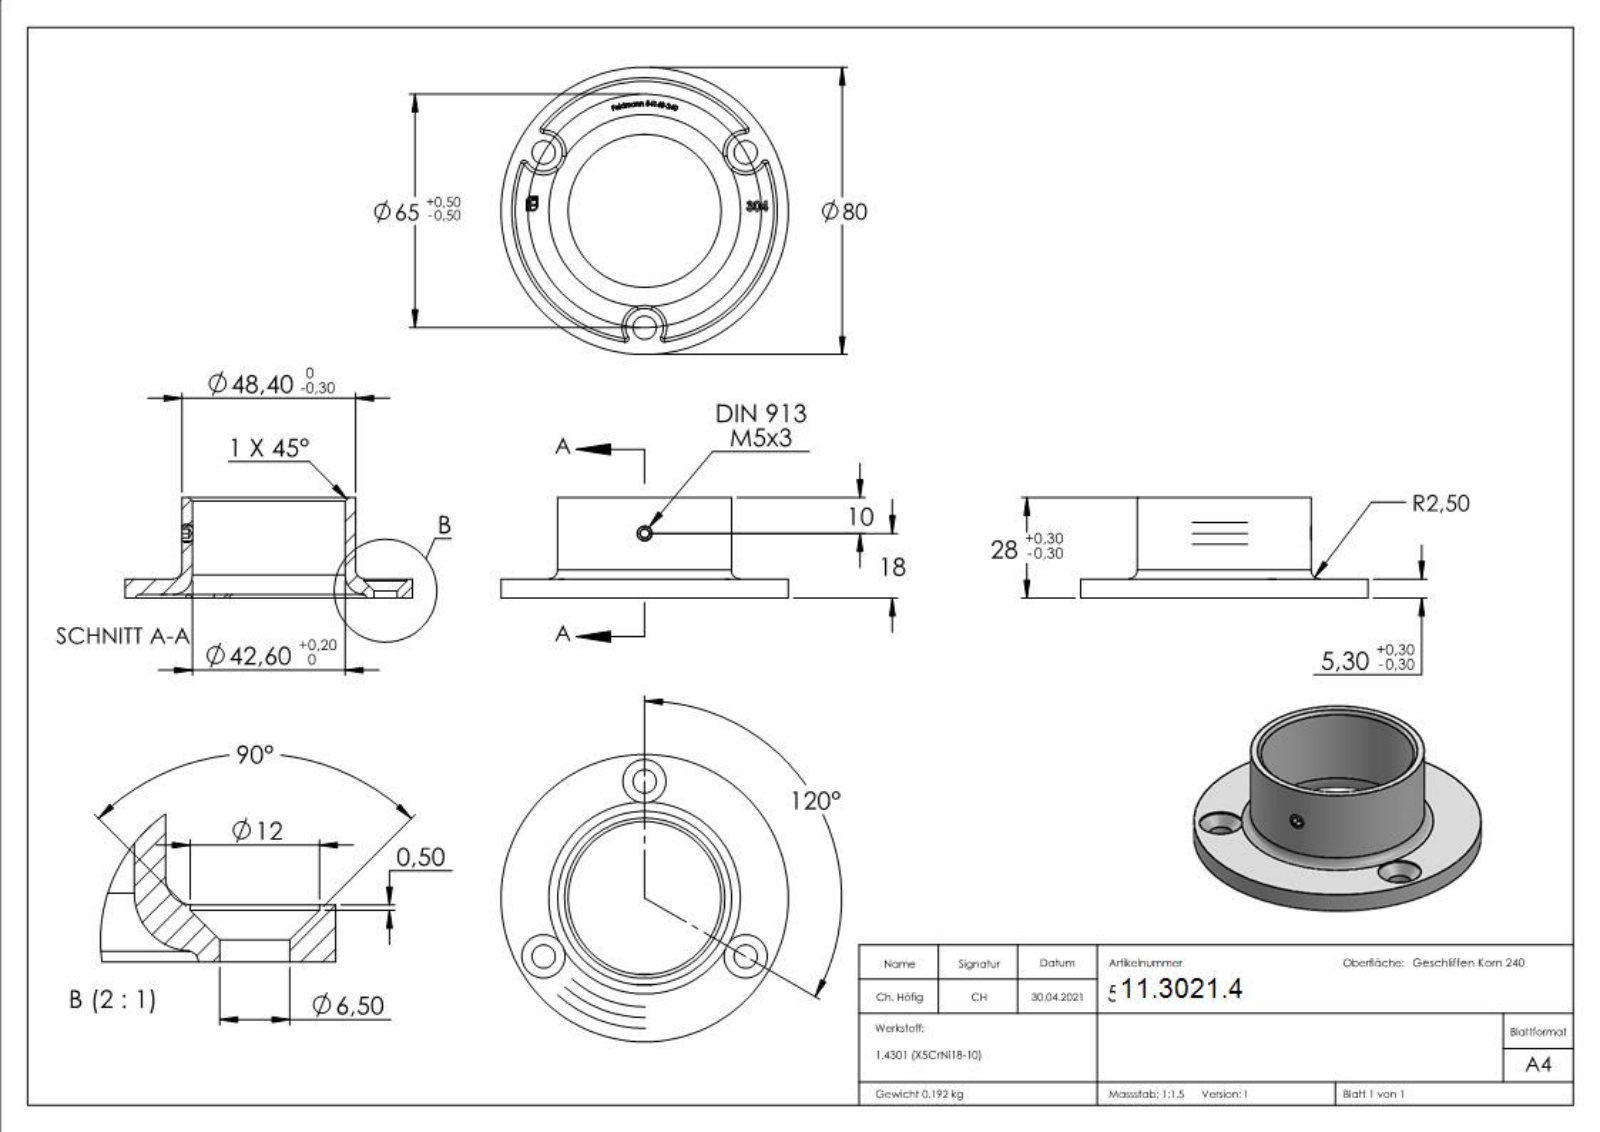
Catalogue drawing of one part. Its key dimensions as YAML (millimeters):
part_name: "54143-240; DIN913; 541XX-240 Teil1_54143-240 Teil1; DIN913_DIN 913 M5x3 (+1 more)"
step_written_by: "SolidWorks 2018 (CONFIG_CONTROL_DESIGN)"
units: millimeters
bodies: {solids: 2, faces: 400, planar: 207, cylindrical: 25, other: 168}
overall_size: [83.8, 80, 28]
volume: 24246
surface_area: 15422
round_holes:
  - {diameter: 6.5, count: 3}
  - {diameter: 12, count: 3}
  - {diameter: 4.2, count: 1}
  - {diameter: 42.6, count: 1}
round_bosses_or_shafts:
  - {diameter: 80, count: 1}
  - {diameter: 48.4, count: 1}
  - {diameter: 5, count: 1}
partial_cylinders:
  - {radius: 5.25, count: 3}
face_to_face_distances: [4.3, 1, 5.3, 28, 27, 22.7, 1.1, 4.2, 26.9, 2.5]
hole_center_spacings: [32.5, 56.29, 56.3]
